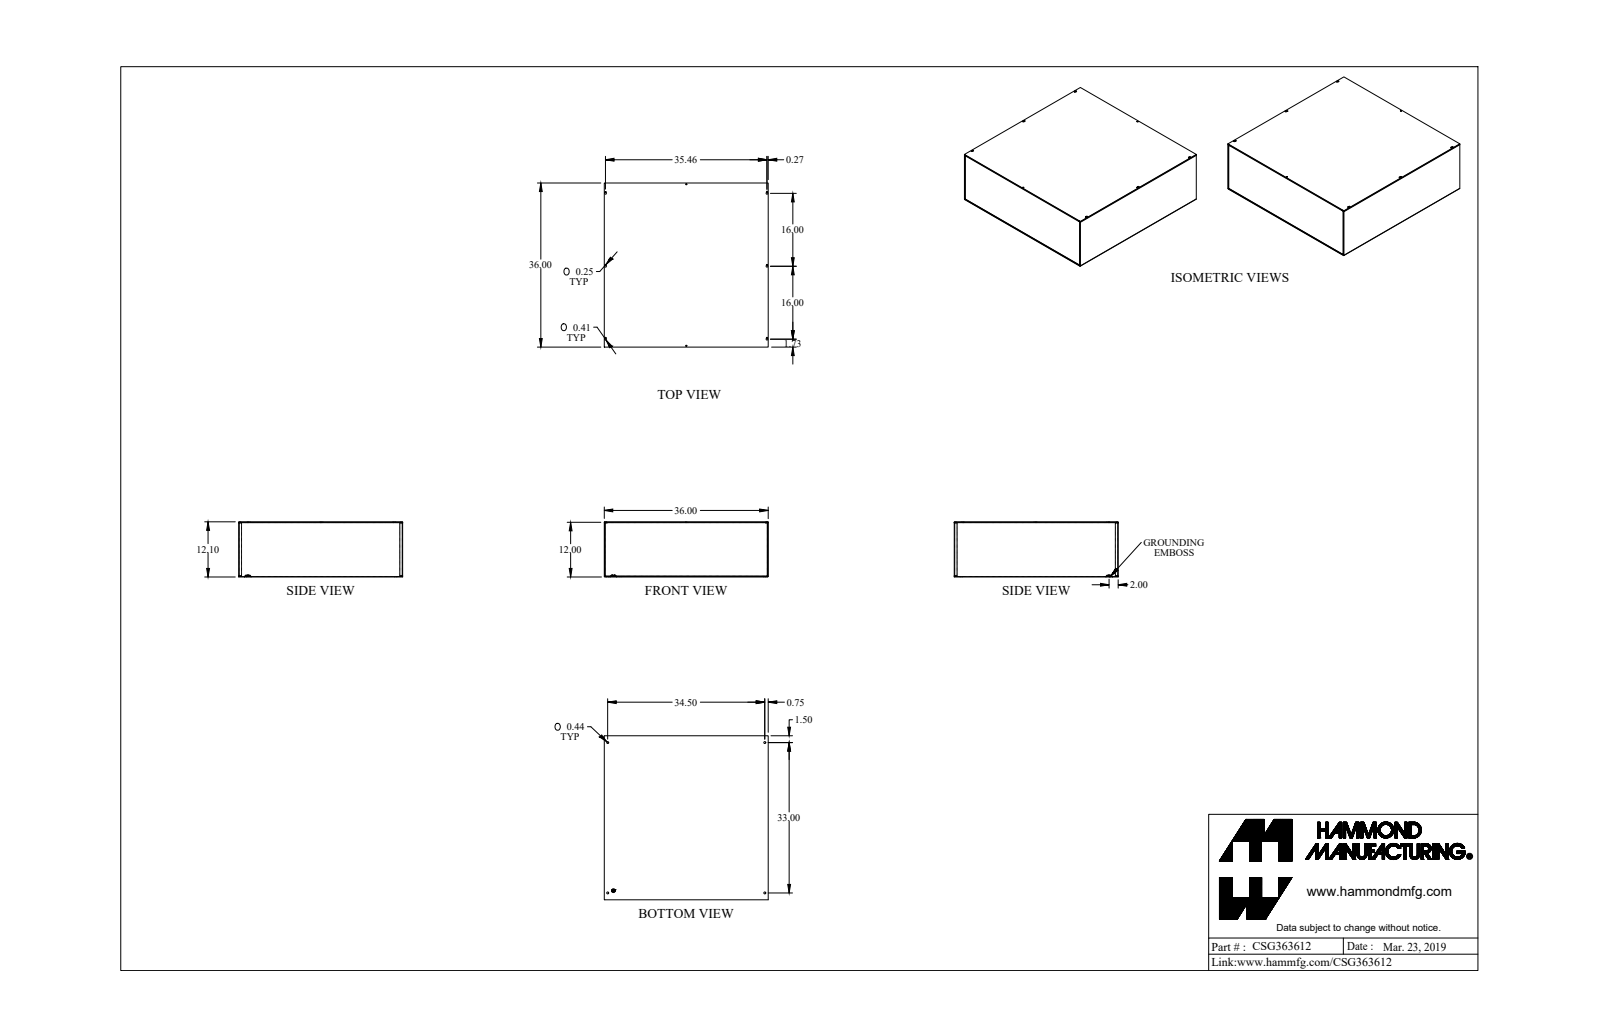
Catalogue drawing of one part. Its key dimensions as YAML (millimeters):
part_name: "CSG363612_Default"
step_written_by: "SolidWorks 2019 (CONFIG_CONTROL_DESIGN)"
units: millimeters
bodies: {solids: 4, faces: 221, planar: 121, cylindrical: 92, other: 8}
overall_size: [914.4, 914.4, 307.2]
volume: 6856000
surface_area: 5717000
round_holes:
  - {diameter: 4.3, count: 9}
  - {diameter: 11.1, count: 4}
  - {diameter: 6.4, count: 2}
  - {diameter: 12.7, count: 1}
round_bosses_or_shafts:
  - {diameter: 12.5, count: 1}
  - {diameter: 9.1, count: 1}
partial_cylinders:
  - {radius: 1.2, count: 12}
  - {radius: 3.6, count: 12}
  - {radius: 2.4, count: 8}
  - {radius: 3.2, count: 6}
  - {radius: 5.2, count: 6}
face_to_face_distances: [2.4, 304.8, 912, 302.4, 307.2, 914.4, 909.6, 4.8, 300, 2.7]
hole_center_spacings: [17.6, 406.4, 419.3, 439.3, 452.5, 636.9, 825.6, 888.6]
